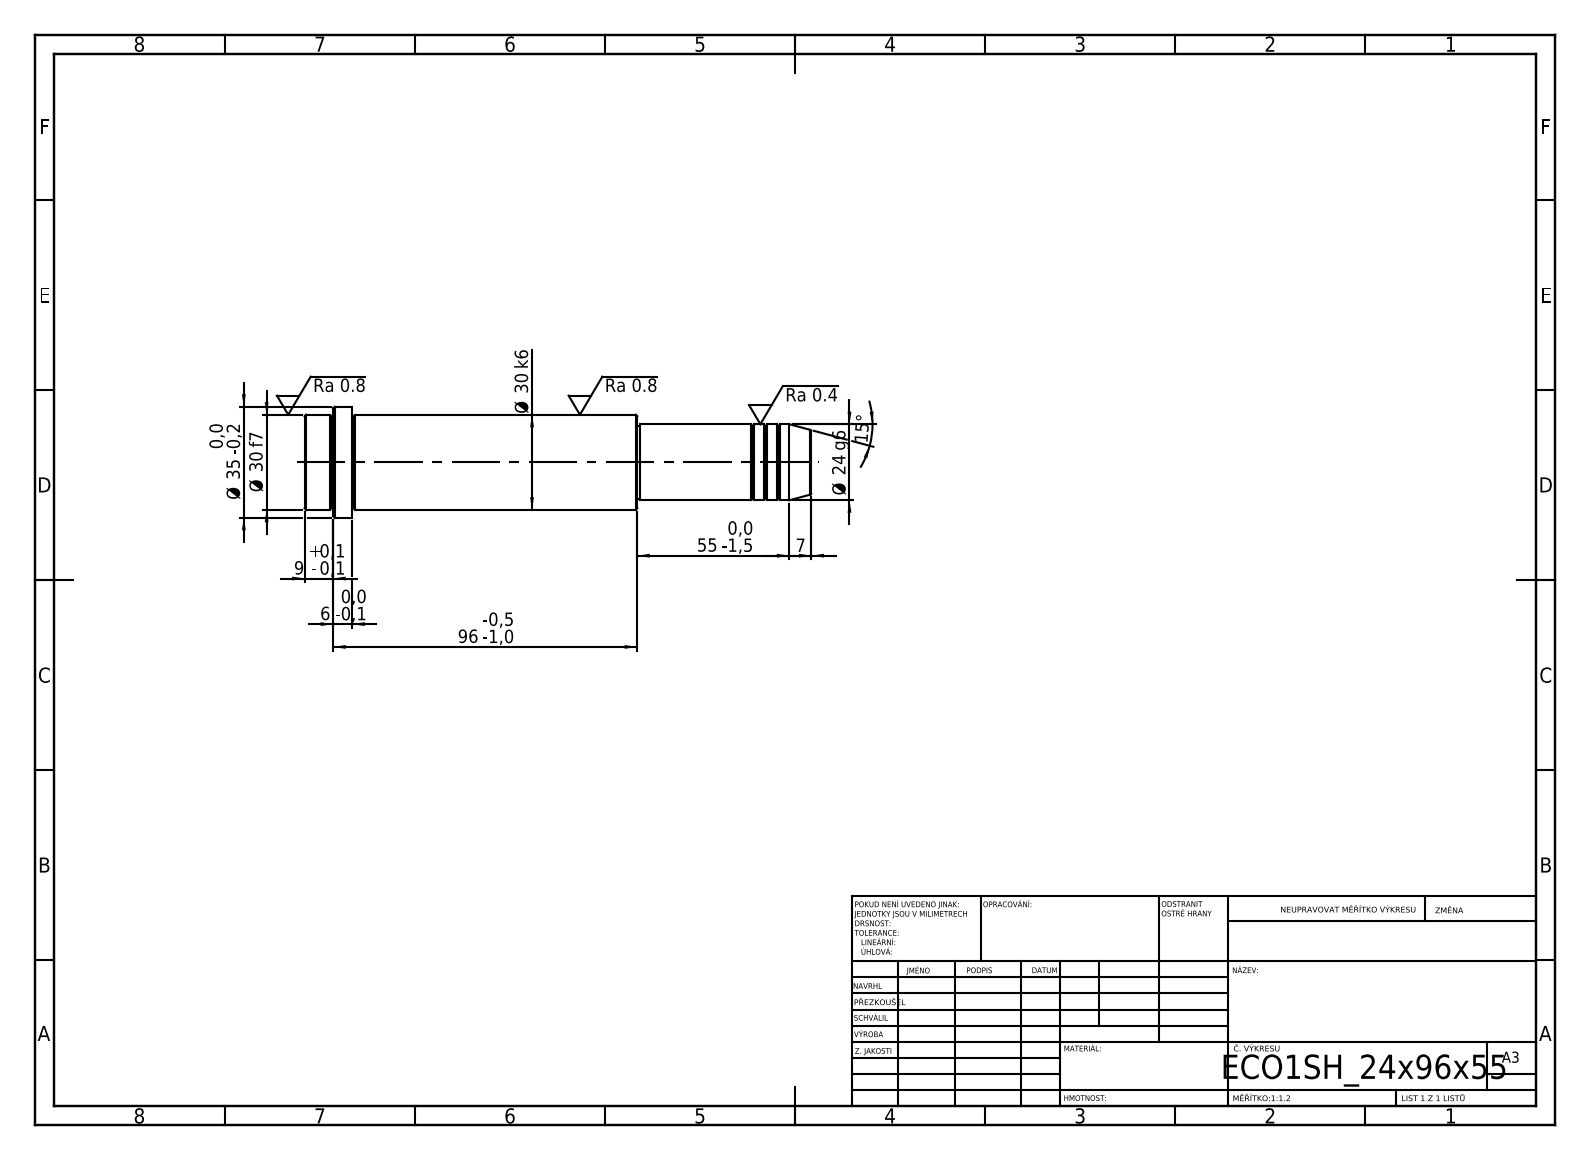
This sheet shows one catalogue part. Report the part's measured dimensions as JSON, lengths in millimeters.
{"step_written_by": "SolidWorks 2019 (CONFIG_CONTROL_DESIGN)", "units": "millimeters", "bodies": {"solids": 1, "faces": 52, "planar": 6, "cylindrical": 16, "other": 30}, "overall_size": [160, 35, 35], "volume_mm3": 99928, "surface_area_mm2": 16103, "round_bosses_or_shafts": [[35, 1], [30, 1], [24, 1], [23, 1]], "face_to_face_distances": [160, 145, 15, 55, 90, 105, 151, 96, 6, 9]}
